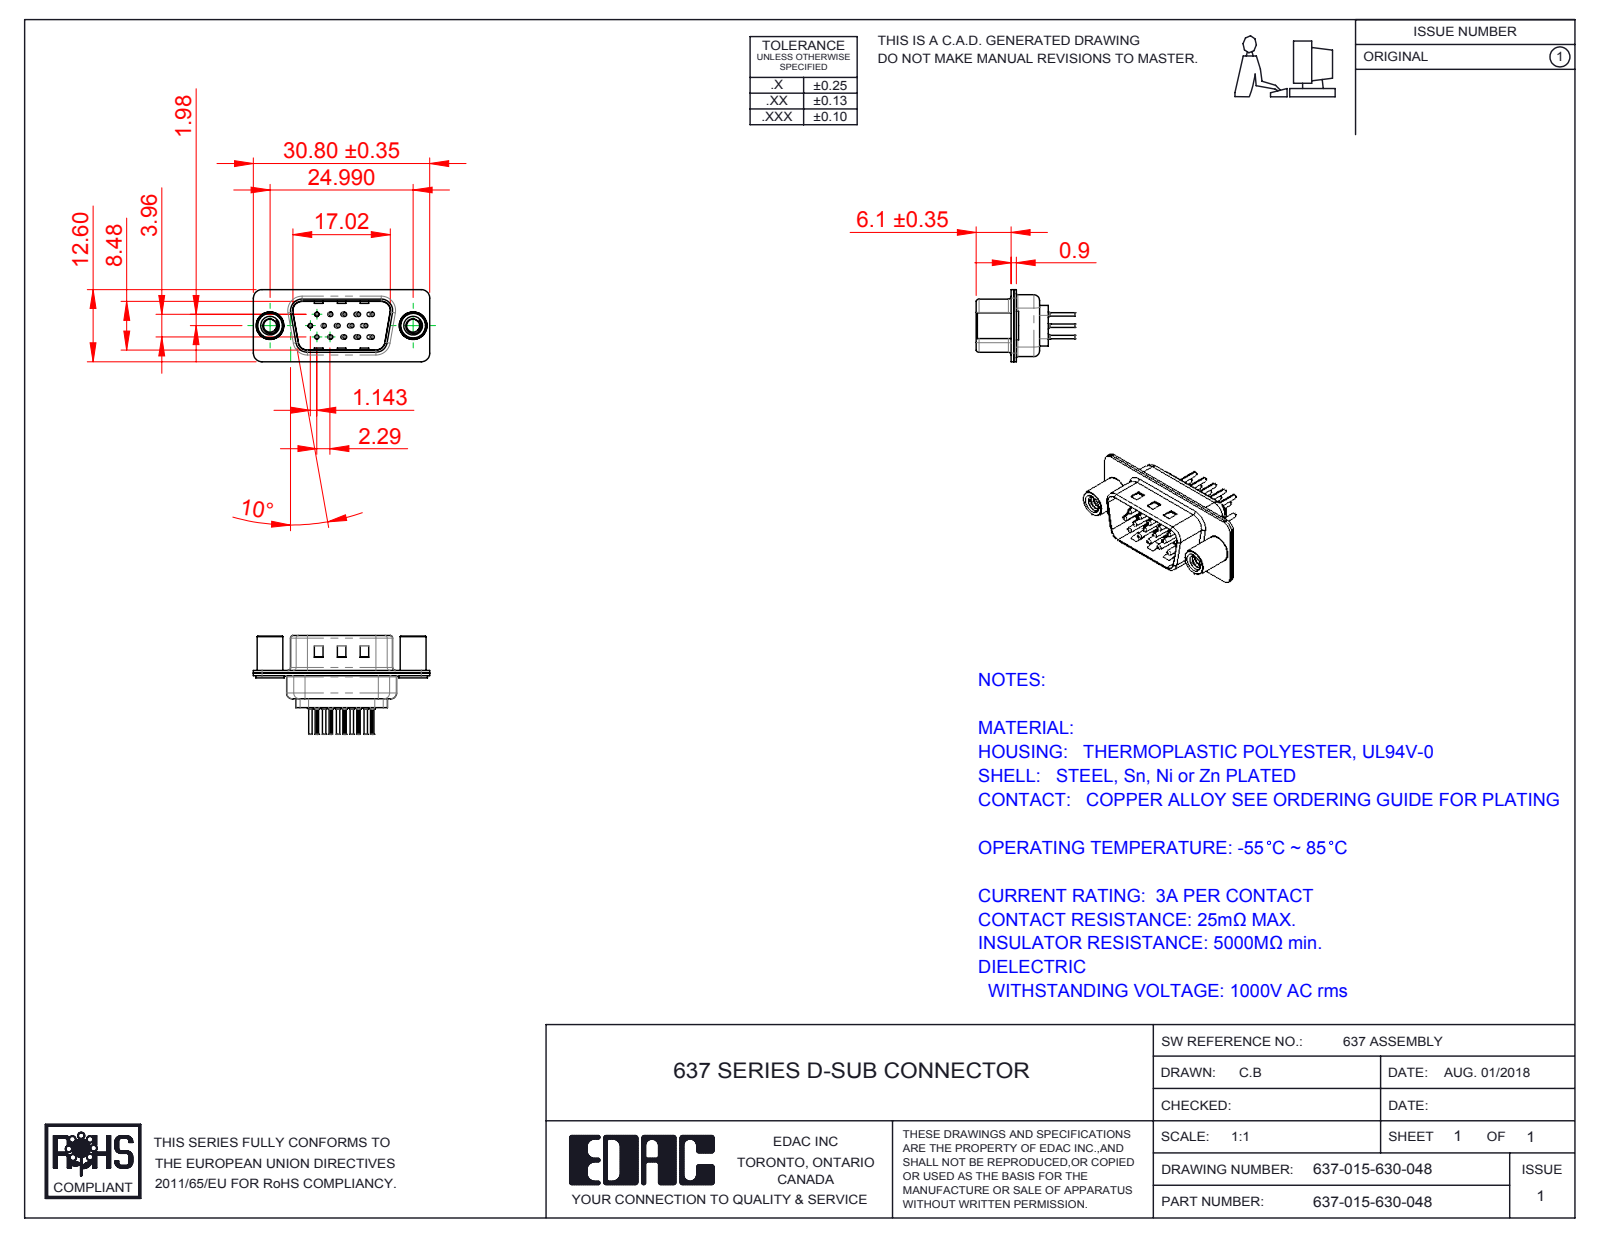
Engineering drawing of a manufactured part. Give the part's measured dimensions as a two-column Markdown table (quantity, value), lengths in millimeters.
| quantity | value |
| --- | --- |
| part name | 637 4-40 Threaded Standoff; 637 Contact Row 3_30; 637 Contact Row 2_30; 637 Contact Row 1_30 (+4 more) |
| STEP written by | SolidWorks 2016 (CONFIG_CONTROL_DESIGN) |
| units | millimeters |
| bodies | 20 solids, 1838 faces (469 planar, 712 cylindrical, 657 other) |
| overall size | 30.8 × 17.25 × 12.6 |
| volume | 1 379 mm³ |
| surface area | 4 840 mm² |
| round holes (diameter × count) | 1.6 × 27, 0.2 × 15, 0.35 × 15, 1.1 × 15, 0.75 × 12, 2 × 12, 2.26 × 2, 4 × 2, 4.8 × 2 |
| round bosses / shafts (diameter × count) | 2 × 15, 1.5 × 15, 0.75 × 15, 0.6 × 15, 5 × 2, 4.9 × 2, 4.5 × 2 |
| partial cylindrical surfaces (radius × count) | 0.1 × 30, 1.5 × 16, 2 × 12, 0.5 × 8, 0.25 × 4, 0.55 × 4, 0.7 × 4, 0.95 × 4 |
| main face-to-face distances | 0.45, 0.9, 0.4, 8.48, 0.7, 8.88, 0.31, 4.55, 1.05, 1.16 |
| hole center spacings | 3.96, 2.29, 2.28, 4.57, 2.42, 6.05, 4.84, 2.35 |
